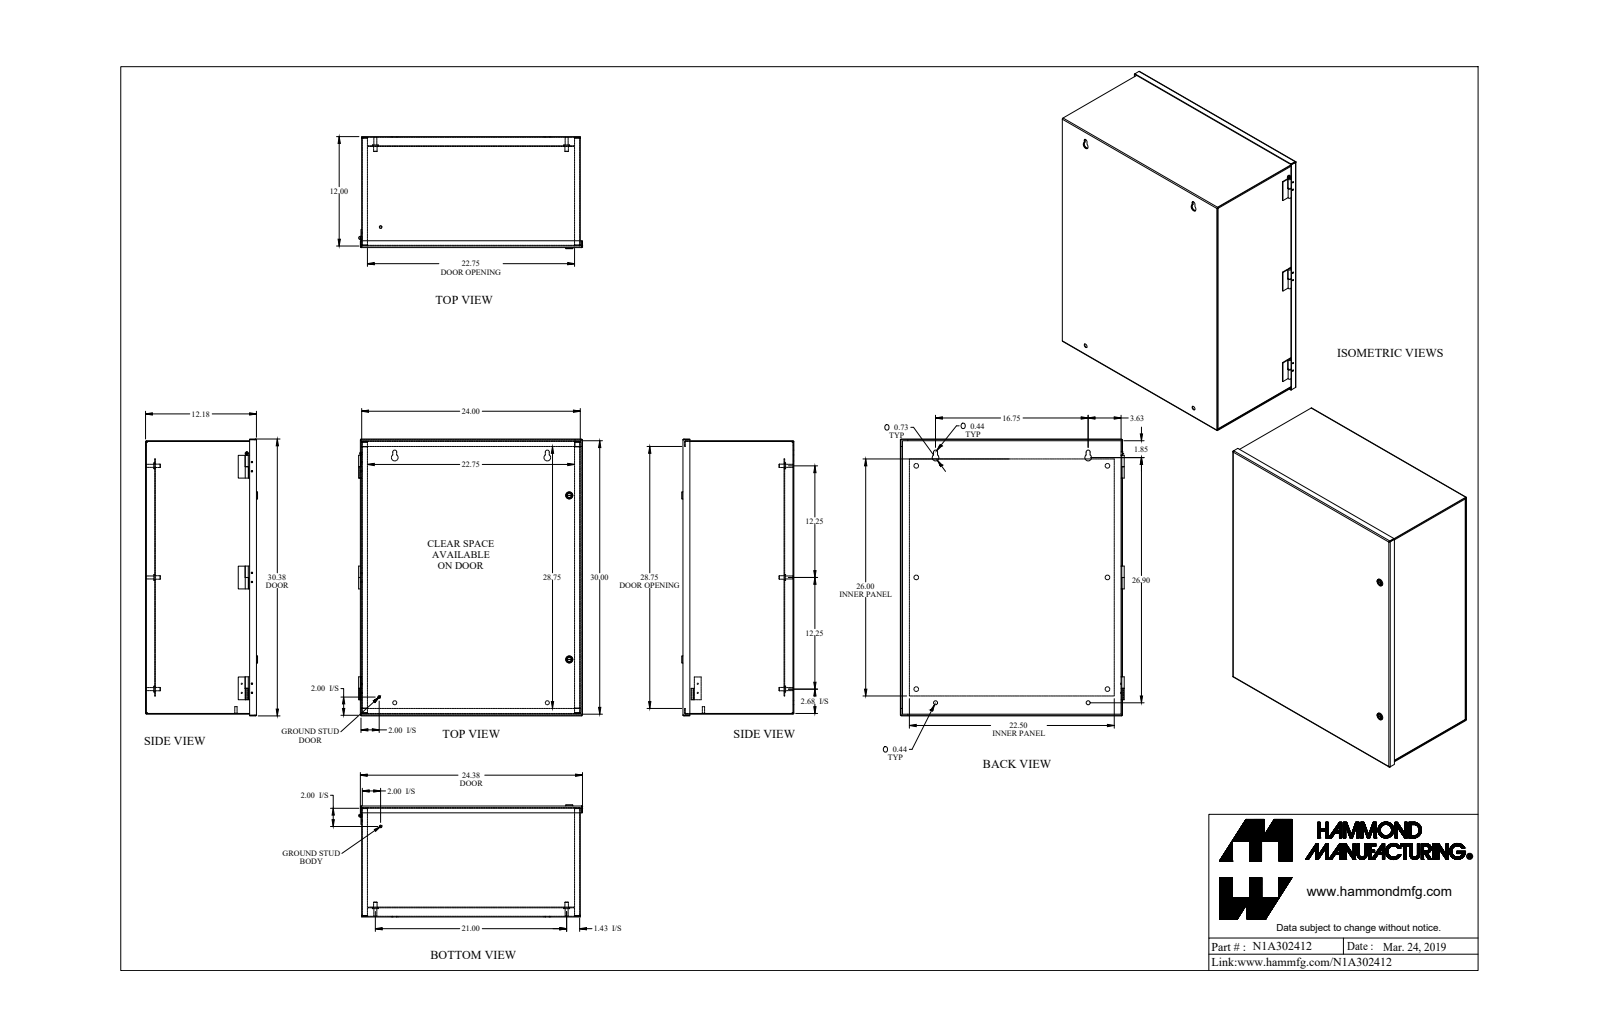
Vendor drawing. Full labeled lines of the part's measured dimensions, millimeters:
Part name (STEP PRODUCT): N1A302412
STEP written by: SolidWorks 2018 (AUTOMOTIVE_DESIGN)
Units: millimetres
Bodies: 34 solids, 767 faces (434 planar, 269 cylindrical, 64 other)
Overall size (bounding box): 771.8 × 624.2 × 312.4
Volume: 4 211 000 mm³ · Surface area: 4 615 000 mm²
Round holes (diameter × count): ⌀3.6 ×12, ⌀12.7 ×6, ⌀7.8 ×4, ⌀11.3 ×4, ⌀11.1 ×2, ⌀13.1 ×2, ⌀18.6 ×2, ⌀4.3 ×1, ⌀4.7 ×1
Round bosses / shafts (diameter × count): ⌀3.3 ×12, ⌀9.5 ×7, ⌀16.5 ×6, ⌀8.4 ×6, ⌀25.4 ×4, ⌀20 ×2, ⌀13.6 ×2, ⌀12.6 ×2
Partial cylindrical surfaces — rounded edges, fillets, slot ends (radius × count): R0.9 ×16, R2.7 ×16, R1.5 ×2, R3.2 ×2, R3.9 ×2, R5.6 ×2, R8 ×2, R0.8 ×1
Main face-to-face distances: 1.8, 307.5, 25.6, 281.8, 305.6, 309.3, 607.8, 23.8, 27.5, 280
Hole centre spacings: 25.4, 28.4, 617.5, 308.8, 308.8, 311.2, 533.4, 82.9
